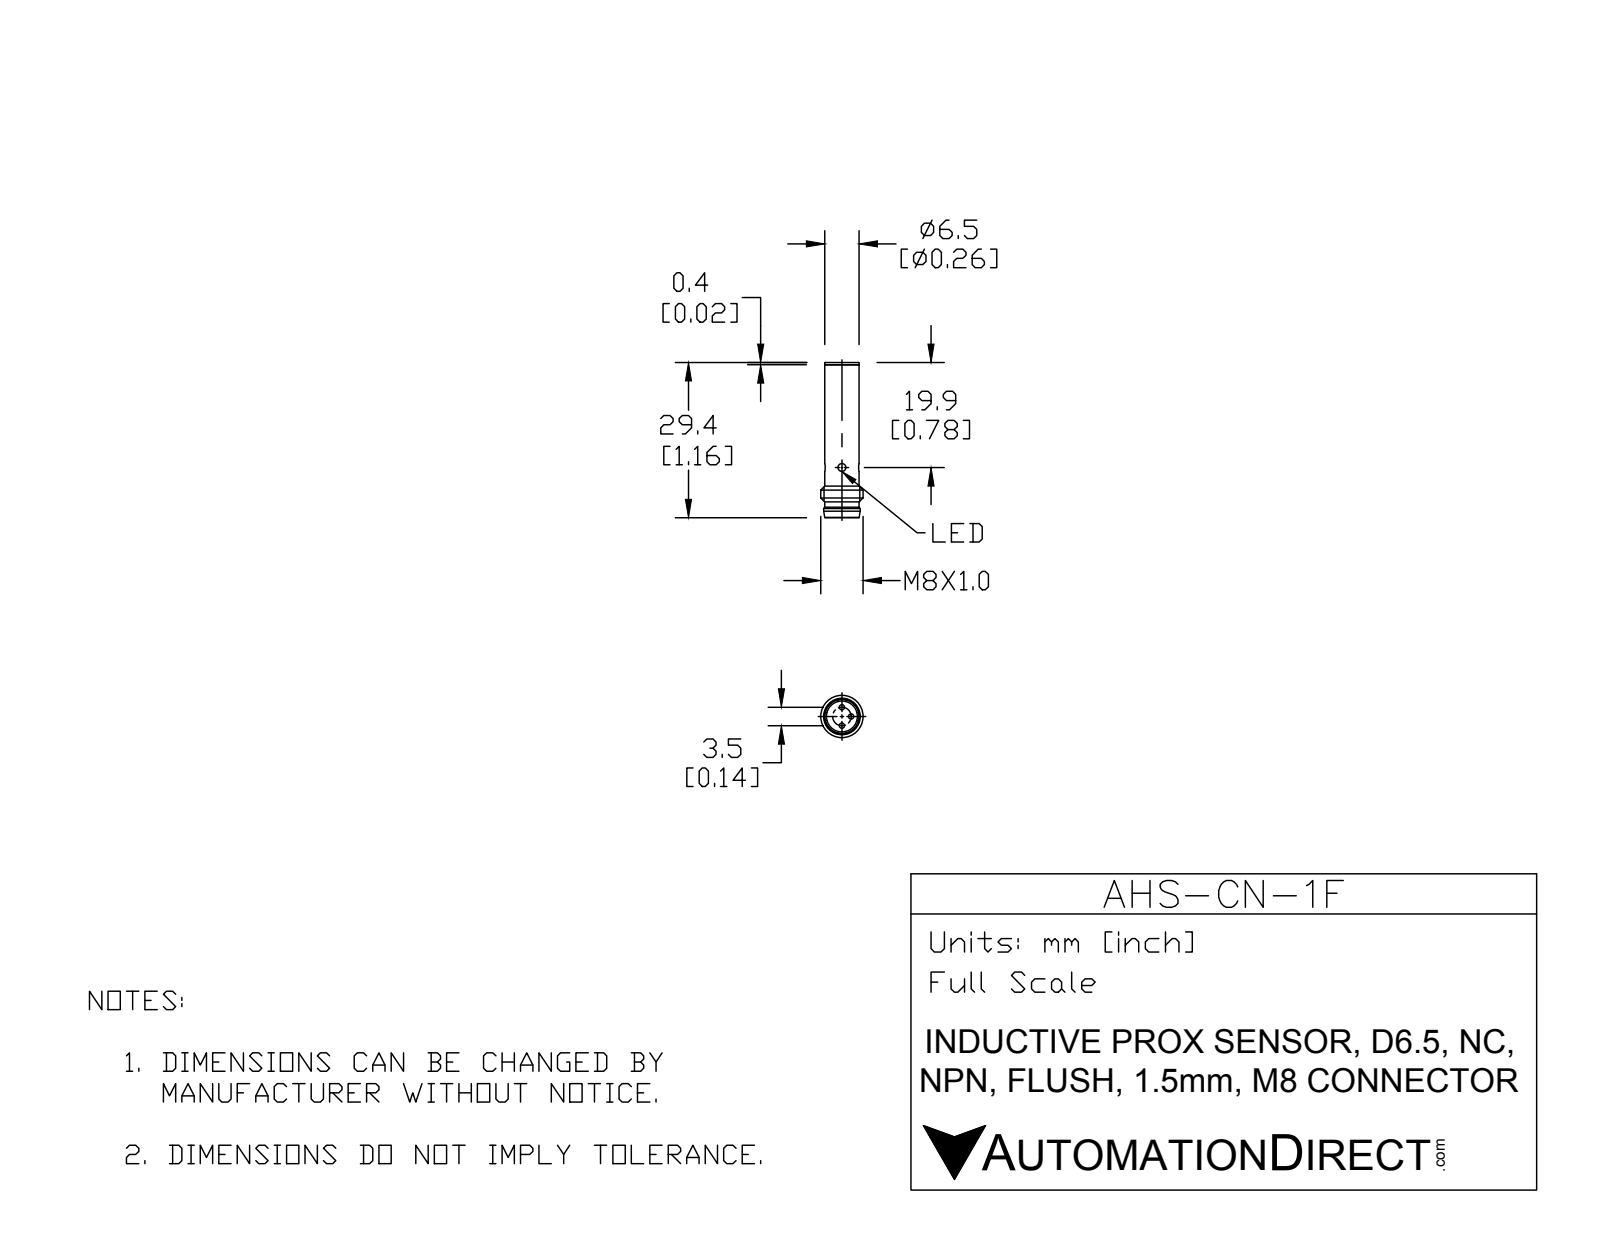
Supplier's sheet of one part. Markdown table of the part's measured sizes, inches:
| quantity | value |
| --- | --- |
| part name | AHS-CN-1F |
| STEP written by | SolidWorks 2015 (CONFIG_CONTROL_DESIGN) |
| units | inches |
| bodies | 4 solids, 56 faces (12 planar, 26 cylindrical, 18 other) |
| overall size | 1.157 × 0.315 × 0.315 |
| volume | 0.054 in³ |
| surface area | 1.31 in² |
| round holes (diameter × count) | 0.059 × 2, 0.23 × 1 |
| round bosses / shafts (diameter × count) | 0.039 × 3, 0.315 × 1, 0.272 × 1, 0.256 × 1 |
| main face-to-face distances | 0.961, 0.118, 1.079, 0.217, 0.079, 0.197, 1.157, 1.142, 1.063, 0.945 |
